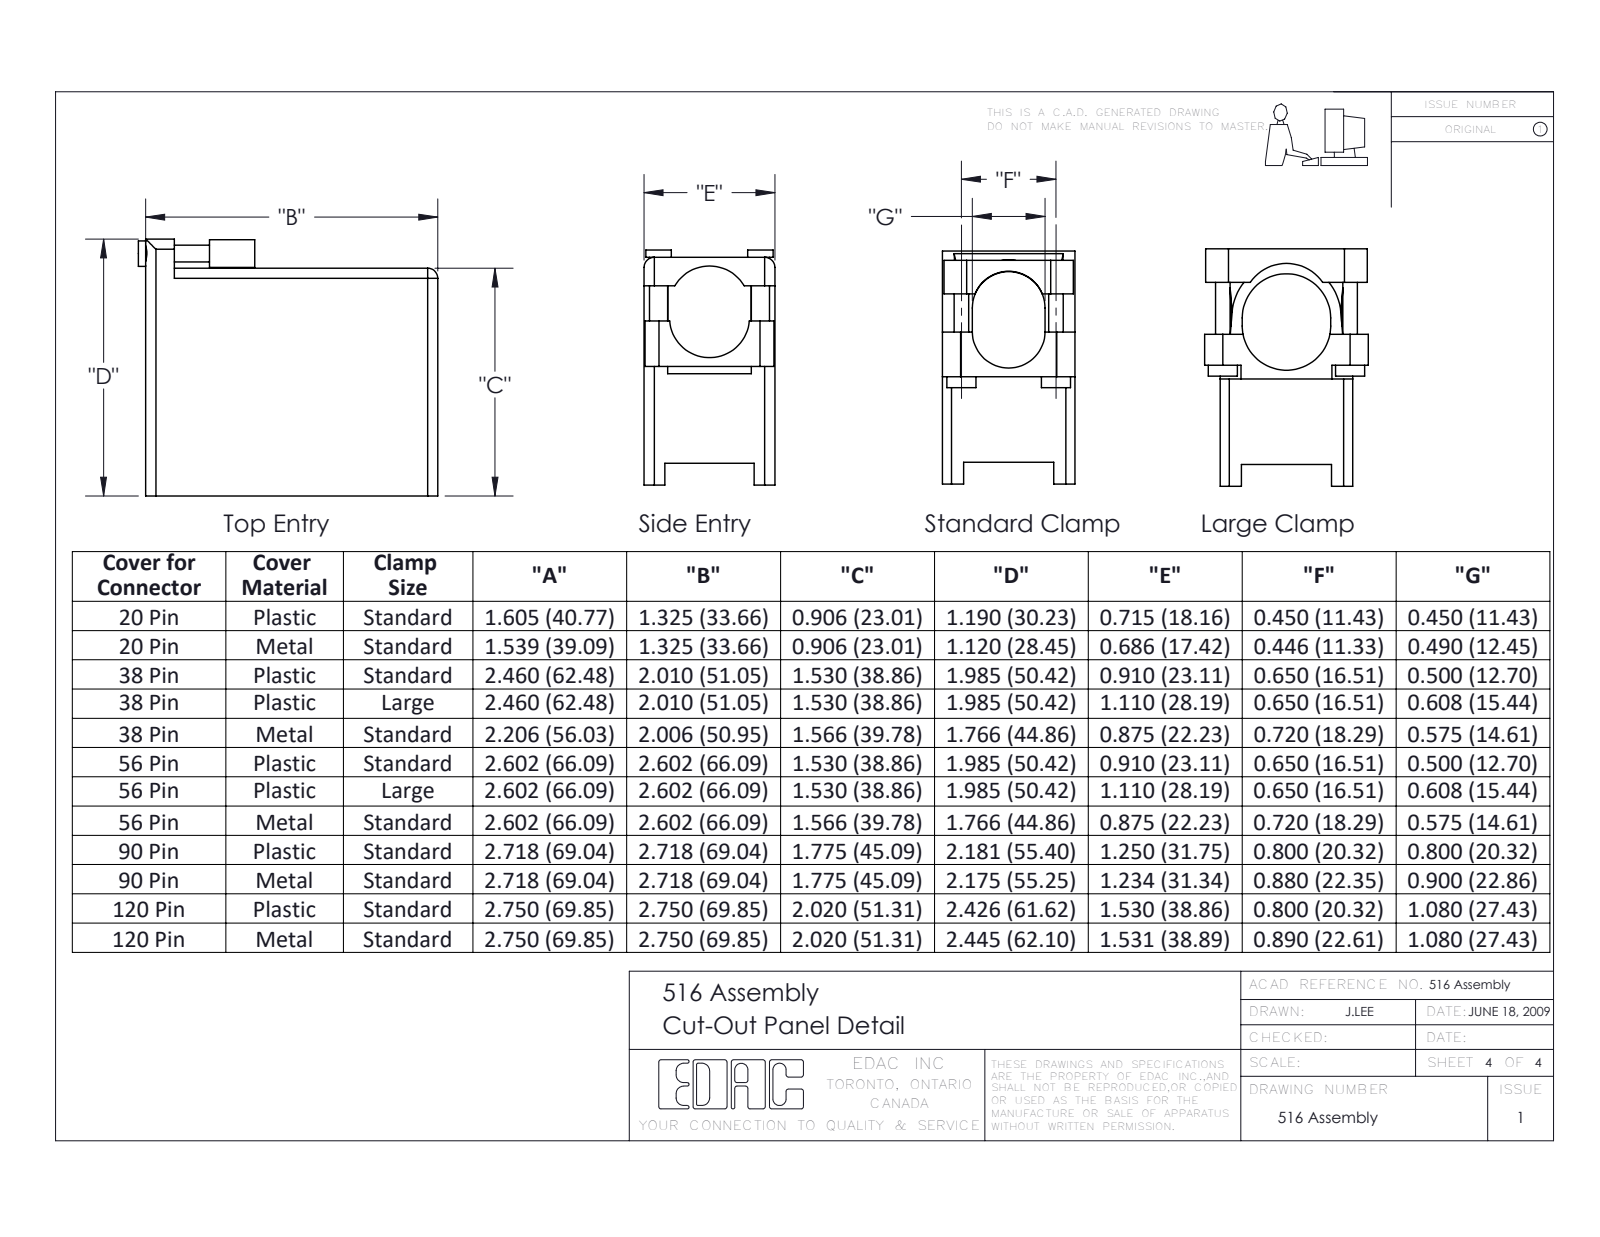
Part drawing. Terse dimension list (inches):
name: 516-253-095-100; 516-254-091-109; 516-292-001_542 Contact; 516-120-542-321 (+8 more)
written by: SolidWorks 2016 (CONFIG_CONTROL_DESIGN)
unit: in
bodies: 133 solids, 11566 faces (7032 planar, 3662 cylindrical, 872 other)
size: 4.501 × 3.155 × 1.53
volume: 3.26 in³; area: 134.4 in²
holes: 120× ⌀0.13, 15× ⌀0.05, 5× ⌀0.145, 4× ⌀0.25, 2× ⌀0.11, 2× ⌀0.133, 2× ⌀0.3, 1× ⌀0.136, 1× ⌀0.145, 1× ⌀0.191, 1× ⌀0.263, 1× ⌀0.325
bosses: 2× ⌀0.28, 2× ⌀0.2, 2× ⌀0.14, 2× ⌀0.138, 2× ⌀0.1, 2× ⌀0.092, 1× ⌀0.313, 1× ⌀0.312
rounds: 270× R0.022, 240× R0.008, 240× R0.016, 60× R0.012, 30× R0.007, 30× R0.08, 22× R0.01, 15× R0.025
face distances: 0.05, 1.48, 0.15, 0.75, 1.43, 0.024, 1.53, 0.3, 0.9, 0.6
hole spacings: 0.3, 0.26, 0.52, 0.15, 0.397, 0.6, 0.13, 0.52
